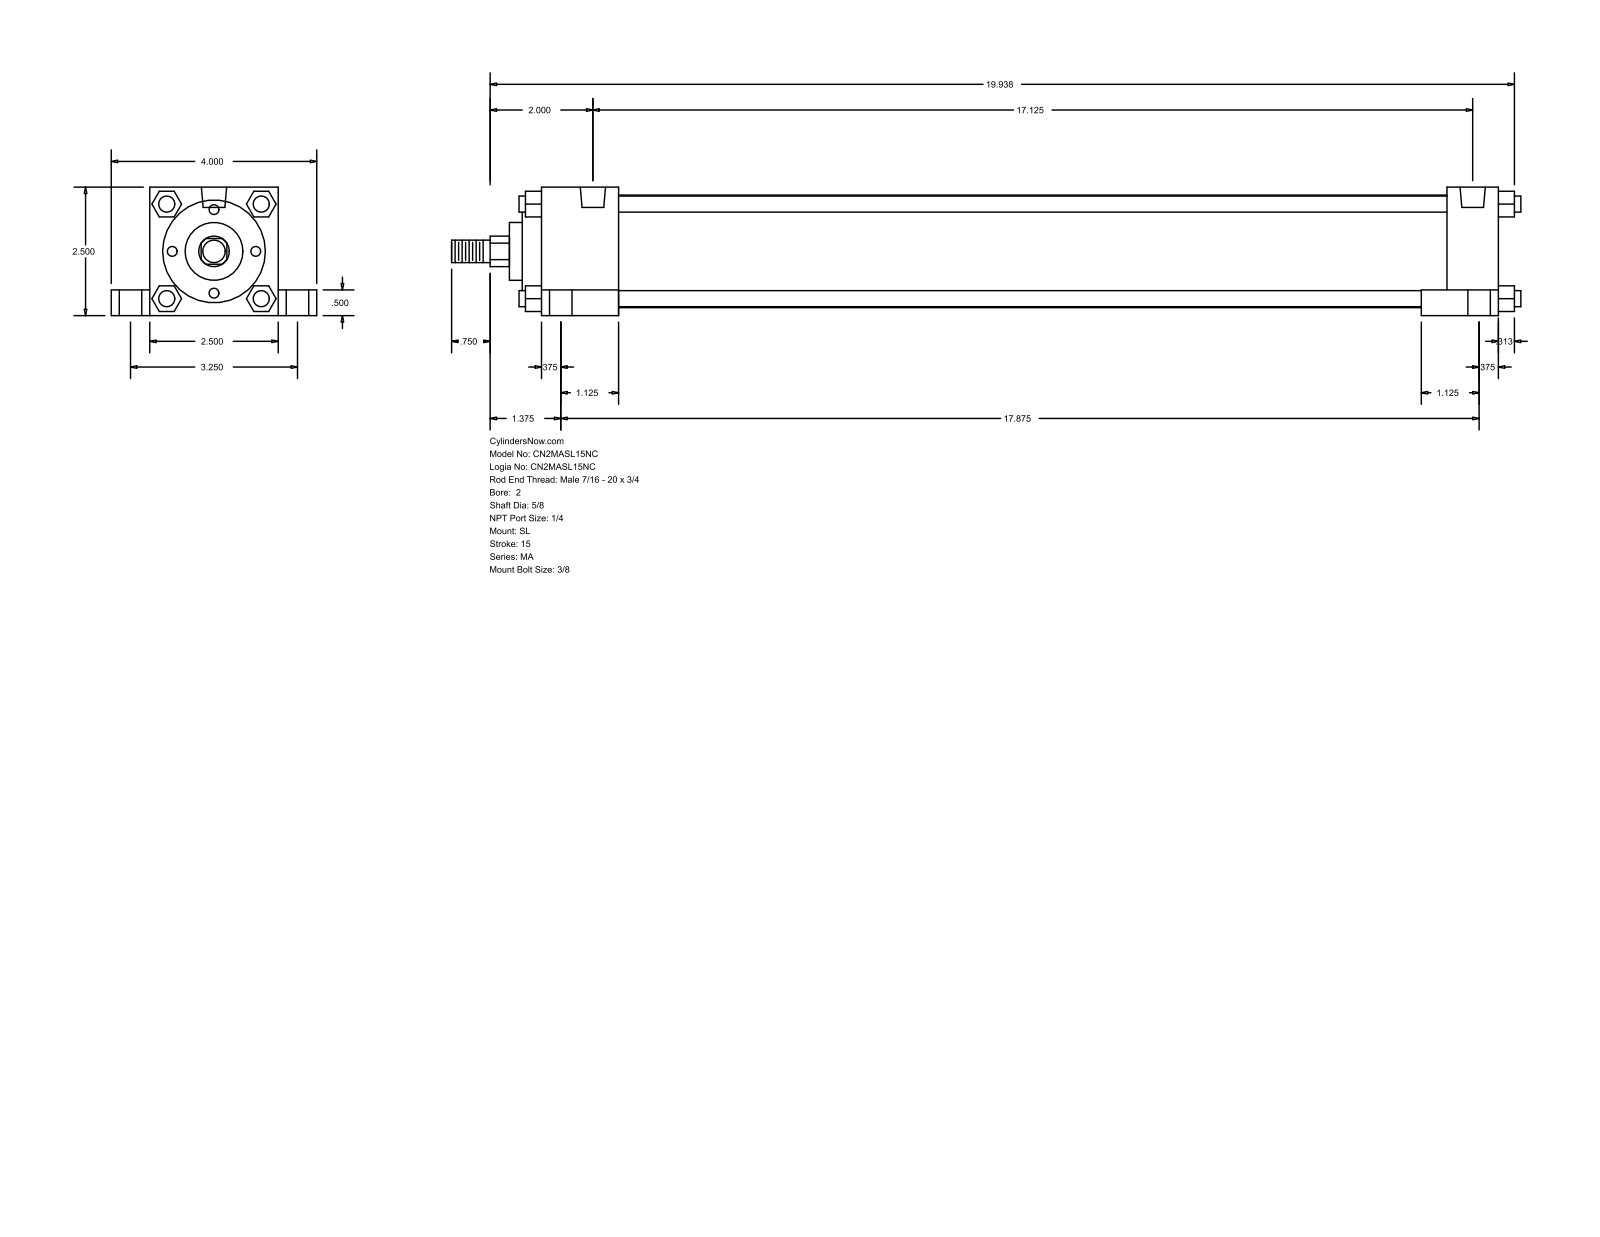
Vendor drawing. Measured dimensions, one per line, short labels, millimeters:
name: MA_SL__0200_0.625
written by: GSSL Pune (CONFIG_CONTROL_DESIGN)
unit: mm
bodies: 0 solids, 150 faces (113 planar, 37 cylindrical, 0 other)
size: 528.64 × 101.6 × 63.5
holes: 4× ⌀7.94, 4× ⌀11.11, 4× ⌀17.46, 2× ⌀12.49
bosses: 4× ⌀7.94, 1× ⌀55.63, 1× ⌀50.8, 1× ⌀28.57, 1× ⌀15.88, 1× ⌀11.11
rounds: 1× R7.54
face distances: 63.5, 12.7, 9.52, 409.57, 19.05, 82.55, 38.1, 50.8, 473.08, 434.98
hole spacings: 41.39, 44.22, 82.54, 434.97, 440.09, 452.73, 454.03, 461.47
